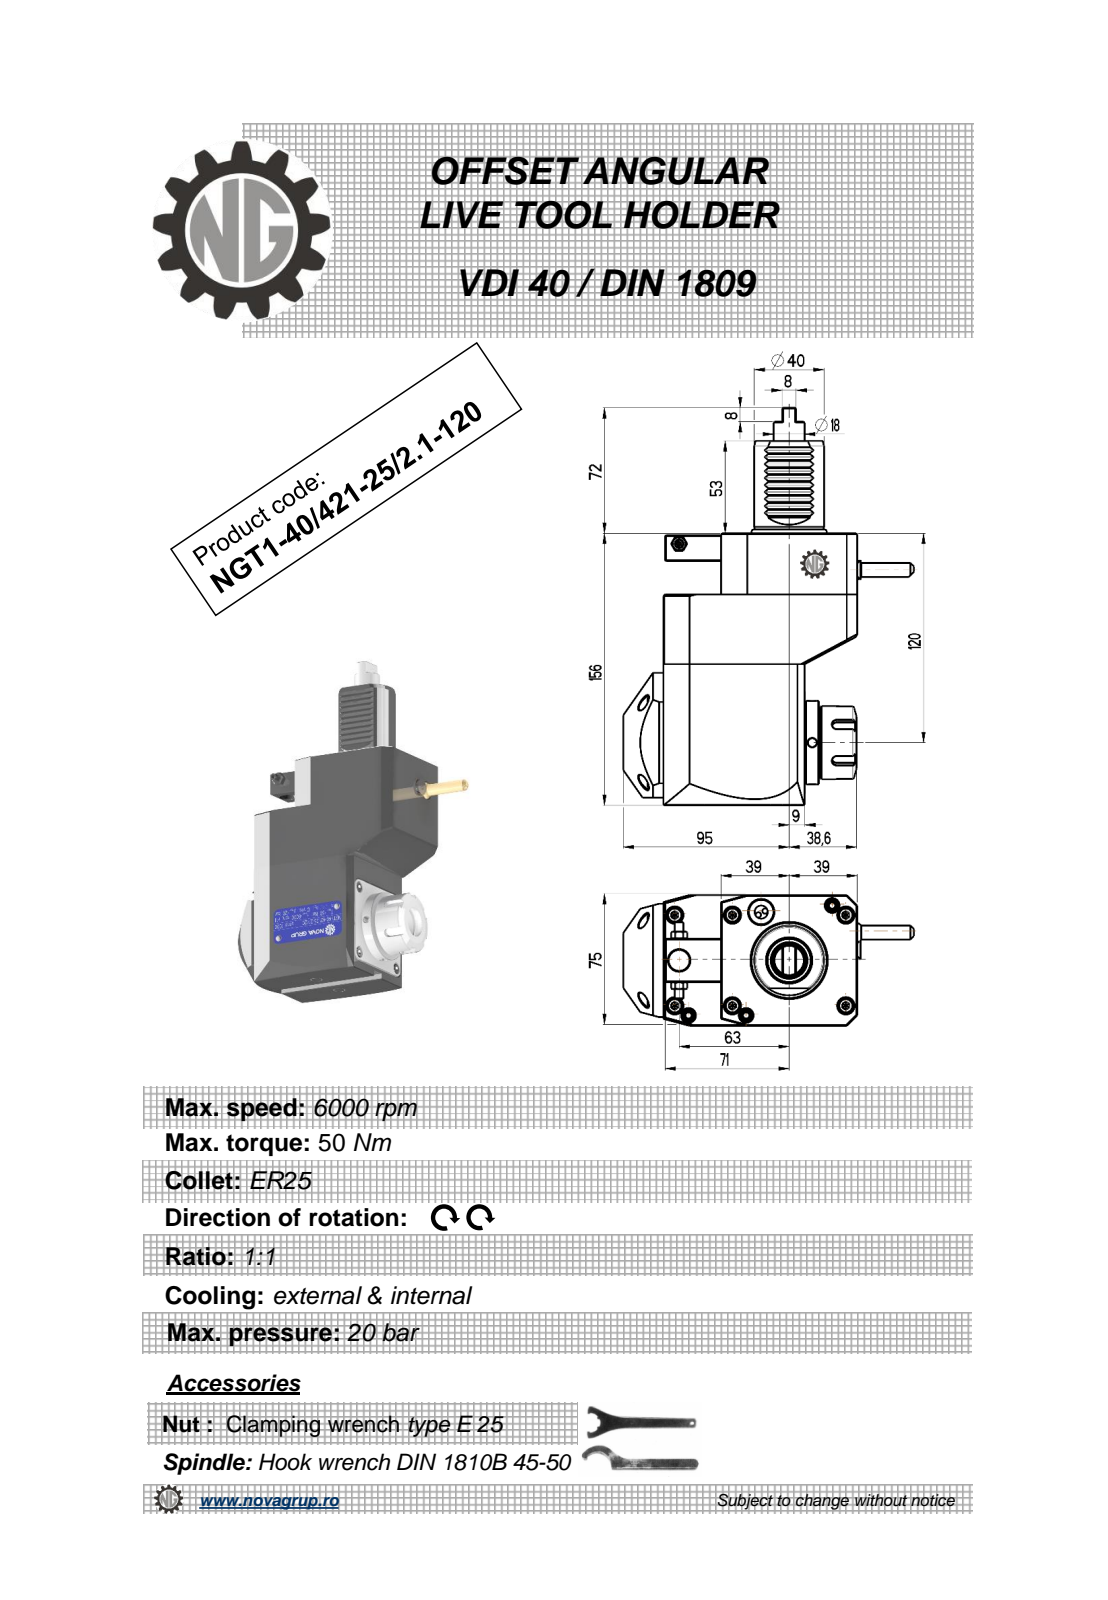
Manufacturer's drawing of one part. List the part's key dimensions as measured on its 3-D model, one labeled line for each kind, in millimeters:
Part name (STEP PRODUCT): NGT1_40_421_25_2_1_120
STEP written by: PRO/ENGINEER BY PARAMETRIC TECHNOLOGY CORPORATION, 2010280 (CONFIG_CONTROL_DESIGN)
Units: millimetres
Bodies: 1 solid, 450 faces (212 planar, 89 cylindrical, 149 other)
Overall size (bounding box): 228 × 166.5 × 76.6
Volume: 1 178 000 mm³ · Surface area: 87 243 mm²
Round holes (diameter × count): ⌀5 ×3, ⌀3 ×1, ⌀4.2 ×1, ⌀9.5 ×1, ⌀12 ×1, ⌀20.3 ×1
Round bosses / shafts (diameter × count): ⌀48 ×1, ⌀42 ×1, ⌀40 ×1, ⌀38 ×1, ⌀33 ×1, ⌀17.8 ×1, ⌀11.2 ×1, ⌀8.96 ×1
Partial cylindrical surfaces — rounded edges, fillets, slot ends (radius × count): R0.26 ×12, R0.3 ×10, R0.22 ×6, R3 ×5, R0.8 ×2, R0.5 ×1, R40 ×1
Main face-to-face distances: 75, 156, 111, 35, 121, 81, 30, 33, 48, 78
Hole centre spacings: 20.93, 76.25, 100.28, 112.5, 137.15
